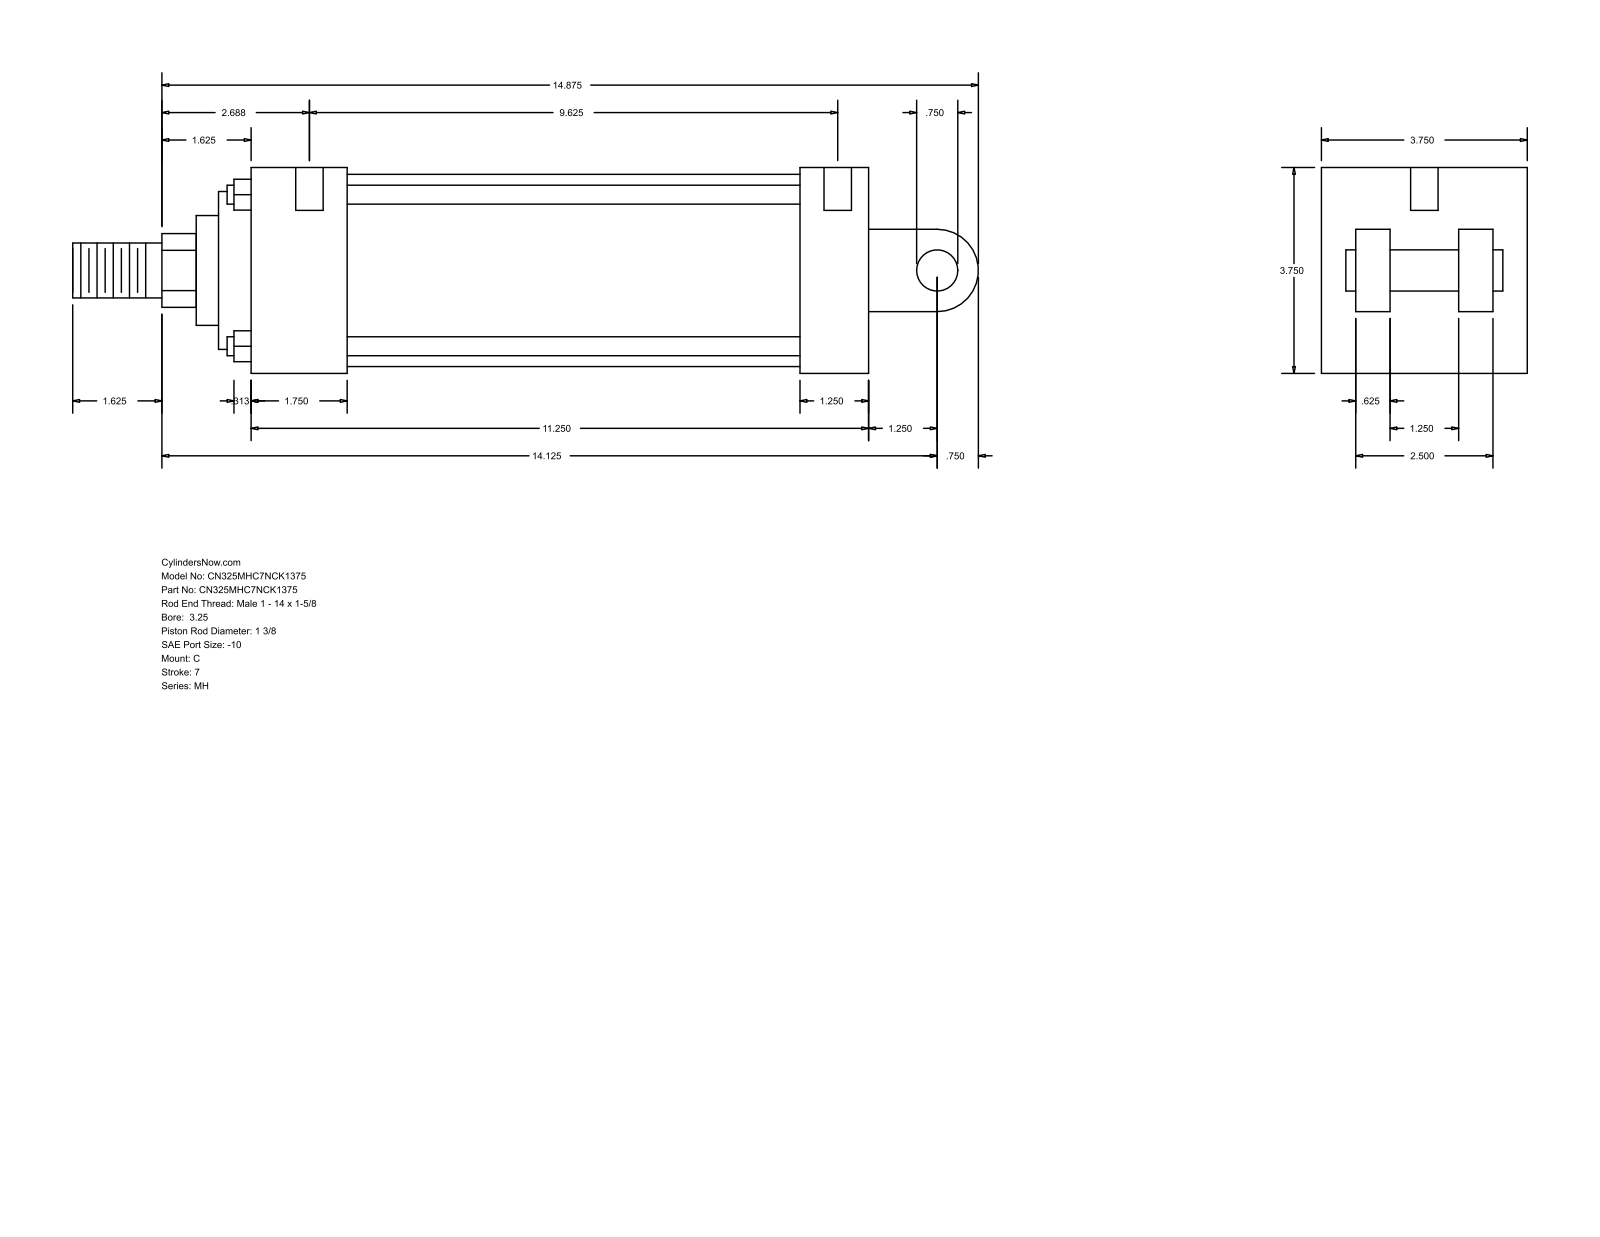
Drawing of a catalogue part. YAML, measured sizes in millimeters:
part_name: "MH_C__0325_1.375"
step_written_by: "GSSL Pune (CONFIG_CONTROL_DESIGN)"
units: millimeters
bodies: {solids: 0, faces: 101, planar: 71, cylindrical: 30, other: 0}
overall_size: [419.1, 95.25, 95.25]
round_holes:
  - {diameter: 5.56, count: 4}
  - {diameter: 12.7, count: 2}
round_bosses_or_shafts:
  - {diameter: 8.76, count: 4}
  - {diameter: 88.9, count: 1}
  - {diameter: 73.03, count: 1}
  - {diameter: 50.8, count: 1}
  - {diameter: 34.92, count: 1}
  - {diameter: 25.4, count: 1}
  - {diameter: 19.05, count: 1}
partial_cylinders:
  - {radius: 17.06, count: 1}
  - {radius: 19.05, count: 1}
face_to_face_distances: [95.24, 15.87, 63.5, 285.75, 79.37, 31.74, 47.63, 44.45, 254, 209.55]
hole_center_spacings: [250.83, 1.59, 4.76, 244.48, 246.07, 249.24]
